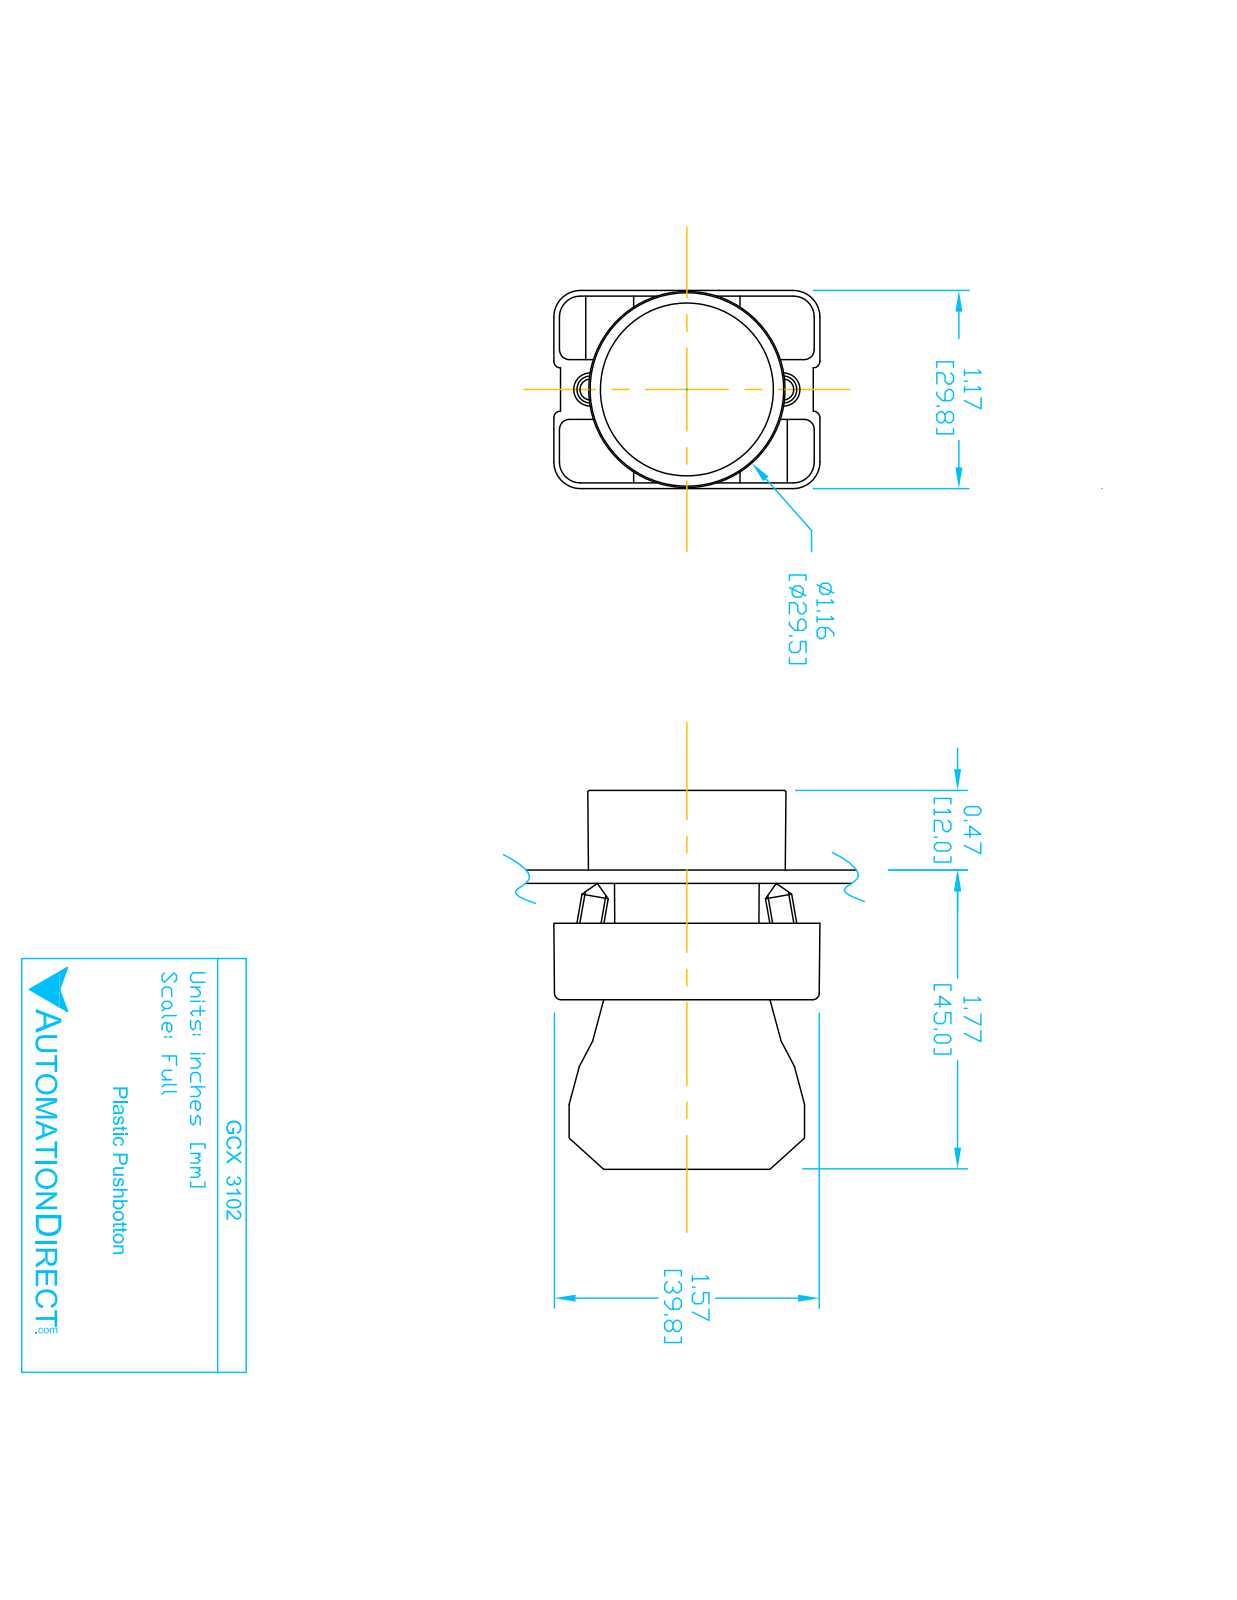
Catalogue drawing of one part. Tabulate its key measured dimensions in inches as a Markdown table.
| quantity | value |
| --- | --- |
| part name | GCX3102; GCX3102 OPERATOR; ECX3029-2; ecx1040 |
| STEP written by | SolidWorks 2016 (AUTOMOTIVE_DESIGN) |
| units | inches |
| bodies | 6 solids, 381 faces (222 planar, 132 cylindrical, 27 other) |
| overall size | 2.217 × 1.581 × 1.177 |
| volume | 1.741 in³ |
| surface area | 27.14 in² |
| round holes (diameter × count) | 0.079 × 2, 0.124 × 2, 0.13 × 2, 0.087 × 1, 0.197 × 1, 0.878 × 1, 0.888 × 1, 1.024 × 1 |
| round bosses / shafts (diameter × count) | 0.157 × 2, 1.175 × 1, 1.004 × 1, 0.945 × 1, 0.856 × 1, 0.78 × 1 |
| partial cylindrical surfaces (radius × count) | 0.059 × 24, 0.041 × 12, 0.124 × 12, 0.157 × 12, 0.039 × 4, 0.128 × 2, 0.02 × 1, 0.063 × 1 |
| main face-to-face distances | 0.72, 0.579, 0.033, 0.472, 1.193, 0.031, 0.689, 0.598, 1.161, 1.071 |
| hole center spacings | 0.236, 0.544, 0.472, 0.49 |
